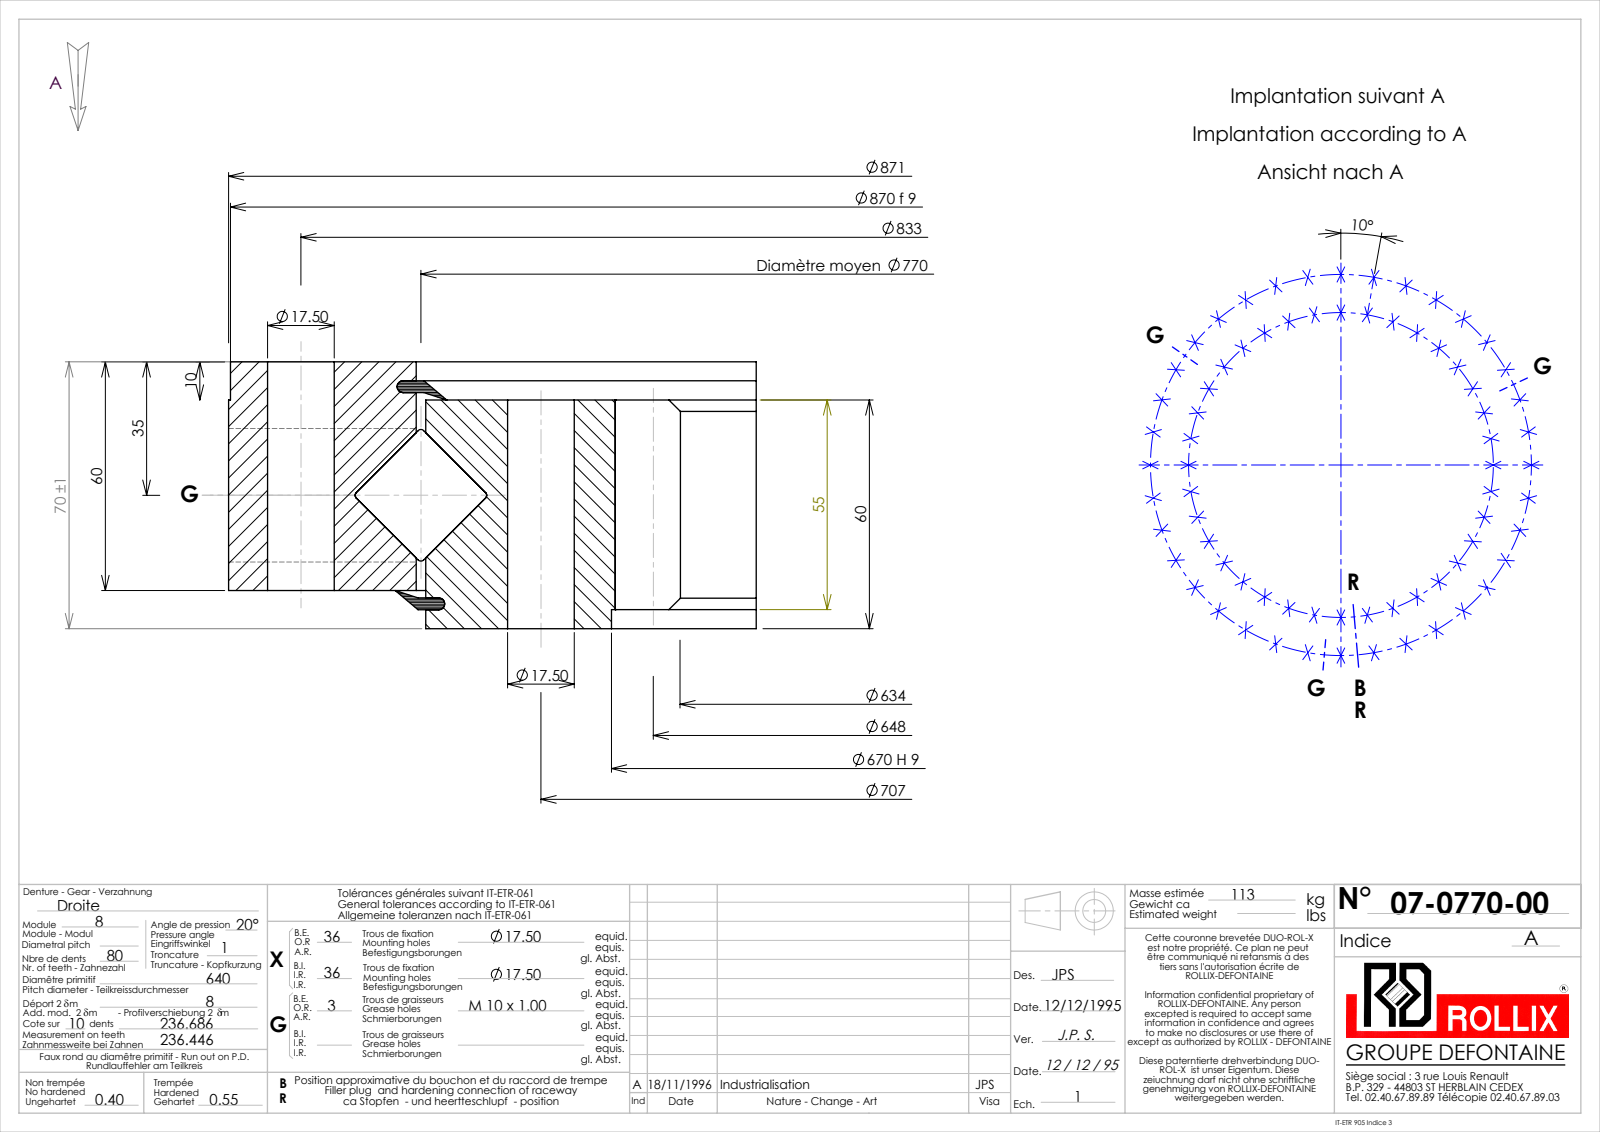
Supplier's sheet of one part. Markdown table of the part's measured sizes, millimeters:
| quantity | value |
| --- | --- |
| part name | 07-0770-00 |
| STEP written by | SolidWorks 2016 (CONFIG_CONTROL_DESIGN) |
| units | millimeters |
| bodies | 5 solids, 711 faces (176 planar, 331 cylindrical, 204 other) |
| overall size | 871 × 871 × 70 |
| volume | 13 110 000 mm³ |
| surface area | 1 652 000 mm² |
| round holes (diameter × count) | 17.5 × 72, 9 × 3, 670 × 1, 772.5 × 1 |
| round bosses / shafts (diameter × count) | 871 × 1, 870 × 1, 767.5 × 1, 25 × 1 |
| partial cylindrical surfaces (radius × count) | 317 × 1, 334 × 1 |
| main face-to-face distances | 10, 60, 50, 70, 4.95, 65.05, 5.05, 55.05, 8.05, 61.95 |
| hole center spacings | 353.5, 122.77, 61.62, 682.91, 696.26, 182.99, 454.45, 704.31 |
